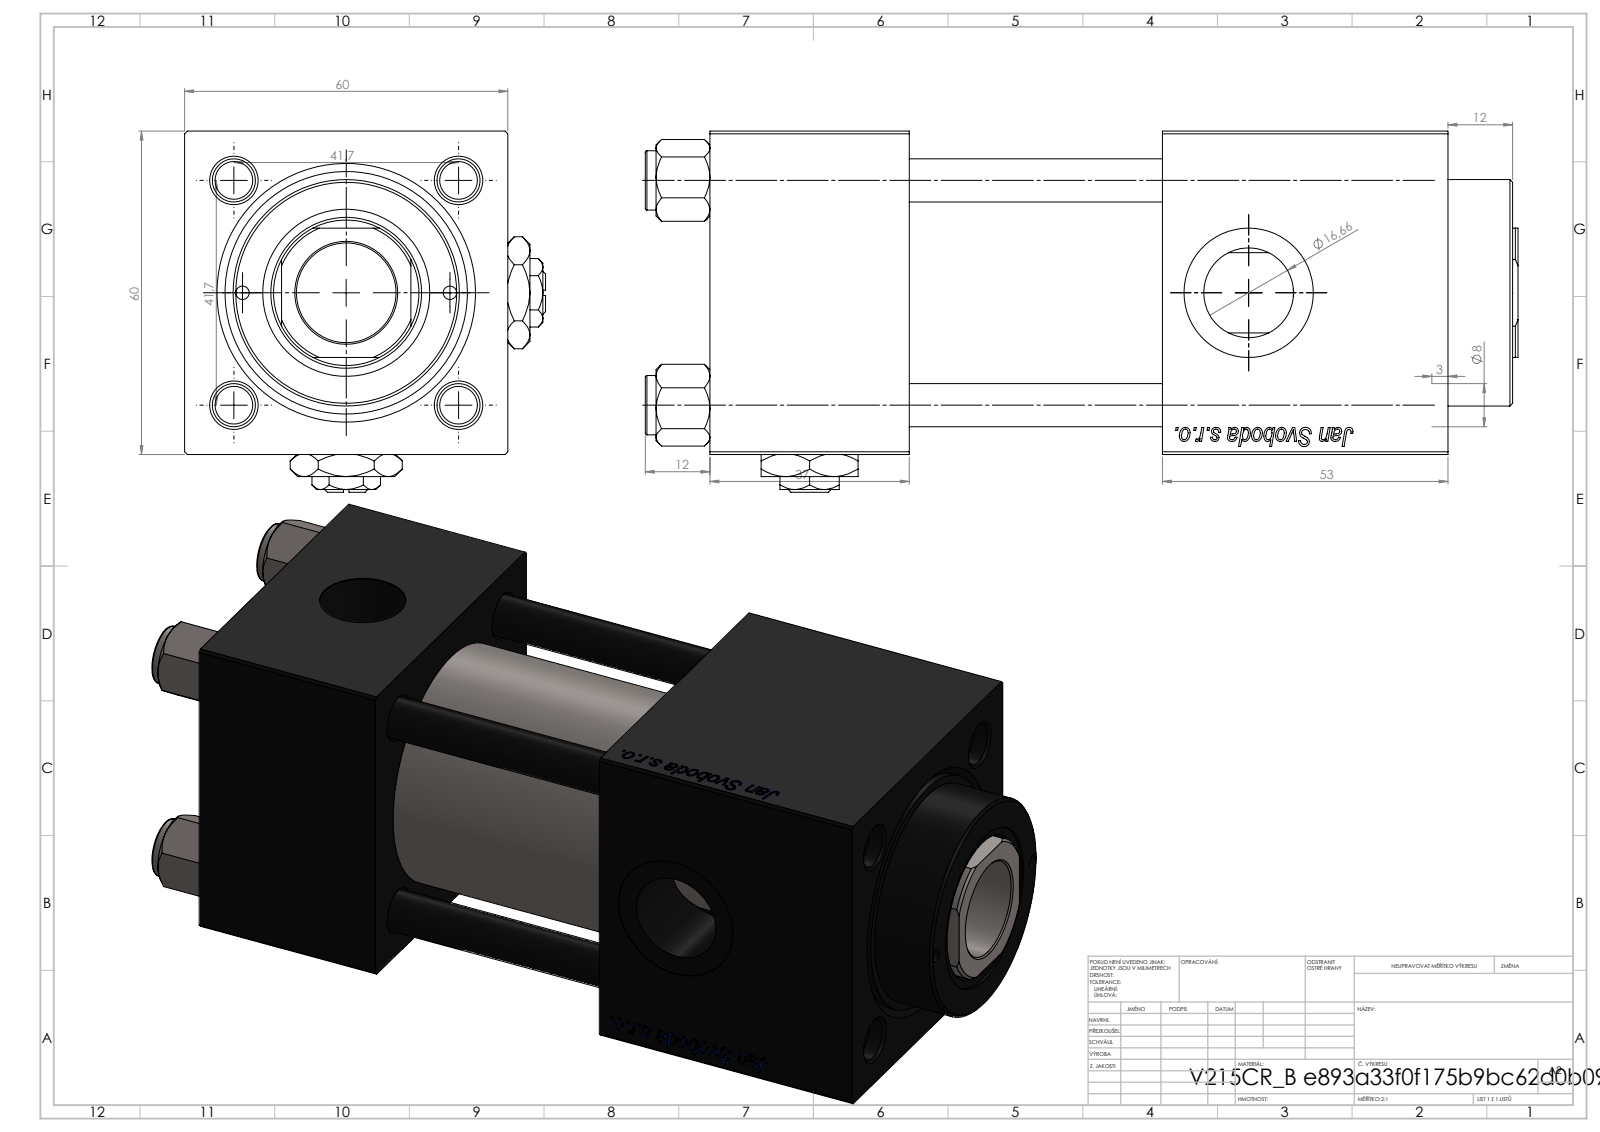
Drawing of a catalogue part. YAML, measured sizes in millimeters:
part_name: "V215CR_VCP_B; Zatka_pro_OIL_PORT; V215CR_B_TYCINKA; V215_VC_A (+2 more)"
step_written_by: "SolidWorks 2019 (CONFIG_CONTROL_DESIGN)"
units: millimeters
bodies: {solids: 13, faces: 1266, planar: 482, cylindrical: 94, other: 690}
overall_size: [162, 67, 67]
volume: 395937
surface_area: 112906
round_holes:
  - {diameter: 8, count: 4}
  - {diameter: 2.5, count: 2}
  - {diameter: 7, count: 2}
  - {diameter: 16.66, count: 2}
  - {diameter: 24, count: 2}
  - {diameter: 16, count: 1}
  - {diameter: 18.5, count: 1}
  - {diameter: 28, count: 1}
  - {diameter: 31, count: 1}
  - {diameter: 40, count: 1}
  - {diameter: 45, count: 1}
round_bosses_or_shafts:
  - {diameter: 11, count: 4}
  - {diameter: 46, count: 1}
  - {diameter: 42, count: 1}
partial_cylinders:
  - {radius: 13.5, count: 1}
face_to_face_distances: [60, 37, 47, 84, 137, 108.3, 71.3, 24.3, 53, 100]
hole_center_spacings: [20.91, 29.49, 41.7, 45.2, 19.25, 58.97, 38.5]
